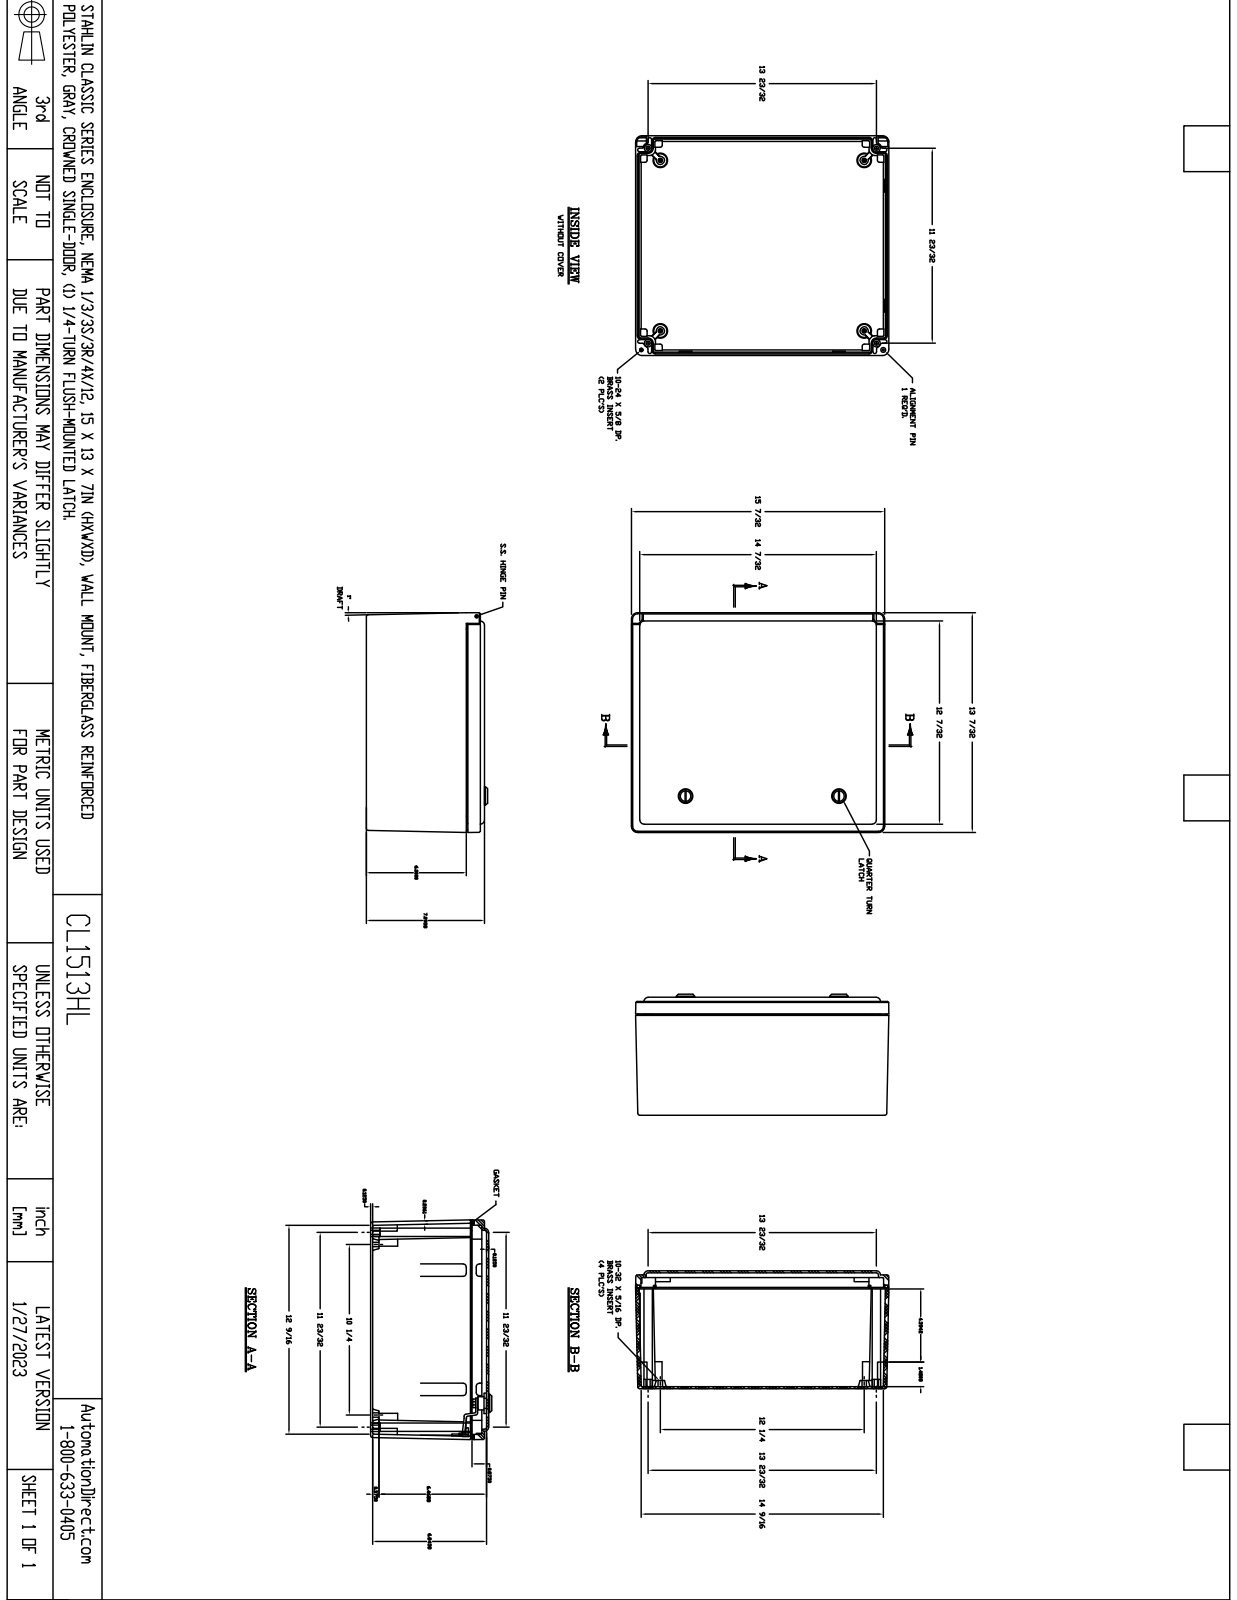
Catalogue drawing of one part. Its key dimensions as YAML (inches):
part_name: "CE1513HL"
step_written_by: "SolidWorks 2018 (AUTOMOTIVE_DESIGN)"
units: inches
bodies: {solids: 37, faces: 1232, planar: 543, cylindrical: 356, other: 333}
overall_size: [15.22, 13.225, 7.281]
volume: 140.4
surface_area: 1712
round_holes:
  - {diameter: 0.281, count: 6}
  - {diameter: 0.104, count: 4}
  - {diameter: 0.13, count: 4}
  - {diameter: 0.14, count: 4}
  - {diameter: 0.156, count: 4}
  - {diameter: 0.313, count: 4}
  - {diameter: 0.531, count: 4}
  - {diameter: 0.096, count: 2}
  - {diameter: 0.145, count: 2}
  - {diameter: 0.15, count: 2}
  - {diameter: 0.156, count: 2}
  - {diameter: 0.219, count: 2}
round_bosses_or_shafts:
  - {diameter: 1.094, count: 2}
  - {diameter: 0.63, count: 2}
  - {diameter: 0.4, count: 2}
  - {diameter: 0.375, count: 2}
  - {diameter: 0.234, count: 2}
  - {diameter: 0.178, count: 2}
  - {diameter: 0.095, count: 2}
  - {diameter: 0.088, count: 2}
partial_cylinders:
  - {radius: 0.031, count: 60}
  - {radius: 0.125, count: 40}
  - {radius: 0.062, count: 23}
  - {radius: 0.313, count: 11}
  - {radius: 0.156, count: 10}
  - {radius: 0.059, count: 8}
  - {radius: 0.063, count: 8}
  - {radius: 0.188, count: 8}
face_to_face_distances: [0.125, 6.969, 0.186, 7.094, 6.844, 0.125, 0.25, 6.844, 6.719, 0.75]
hole_center_spacings: [1.039, 11.01, 13.007, 17.009, 8.688, 0.014, 0.528, 0.572]
